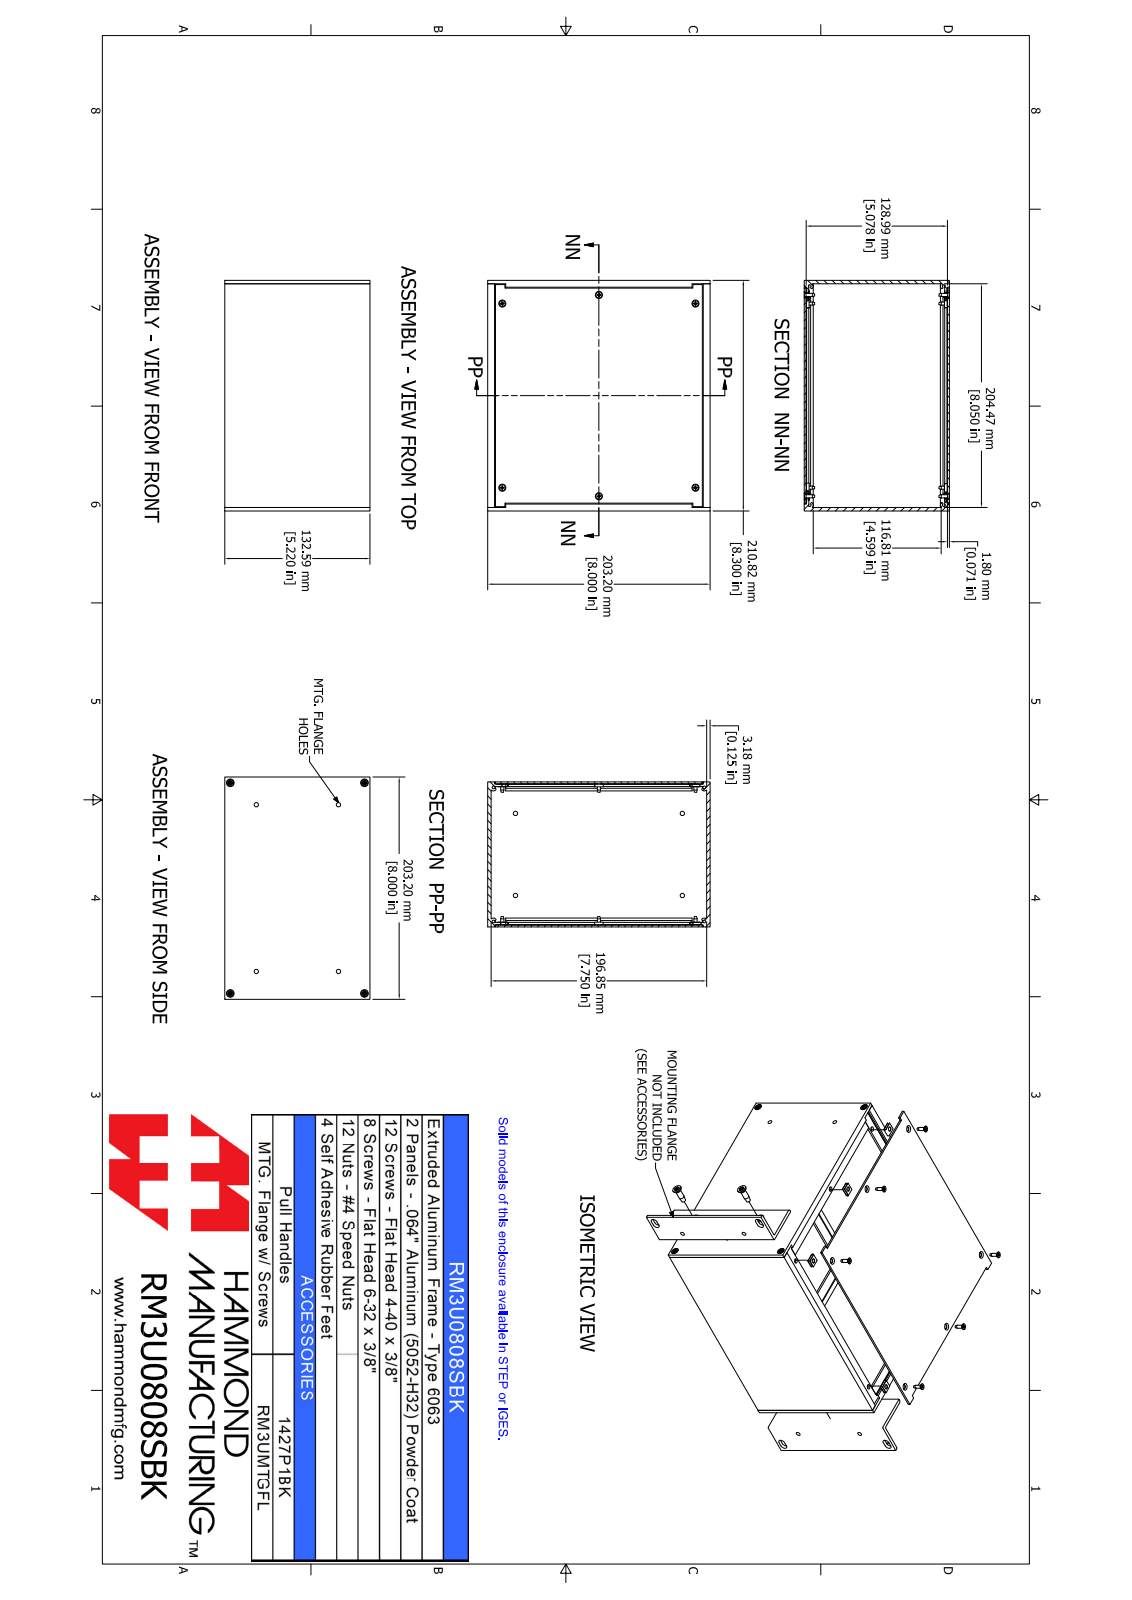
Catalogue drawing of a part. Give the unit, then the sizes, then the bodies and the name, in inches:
Units: inches
Overall size (bounding box): 8.3 × 8 × 5.22
Round holes (diameter × count): ⌀0.098 ×6, ⌀0.157 ×6, ⌀0.169 ×6, ⌀0.138 ×4, ⌀0.156 ×4
Round bosses / shafts (diameter × count): ⌀0.214 ×6, ⌀0.112 ×6, ⌀0.238 ×4, ⌀0.138 ×4
Partial cylindrical surfaces — rounded edges, fillets, slot ends (radius × count): R0.039 ×12, R0.049 ×12, R0.037 ×8, R0.05 ×8, R0.125 ×8, R0.038 ×4
Main face-to-face distances: 0.071, 5.149, 0.125, 0.125, 5.22, 5.078, 8, 8.3, 8.05, 7.75
Hole centre spacings: 3.486, 6.854, 7.824, 1.224, 1.224, 2.953, 3.967, 3.968
Volume: 33.21 in³ · Surface area: 674.5 in²
Bodies: 38 solids, 976 faces (468 planar, 156 cylindrical, 352 other)
Part name (STEP PRODUCT): RM3U0808SBK
STEP written by: SolidWorks 2021 (AUTOMOTIVE_DESIGN)
